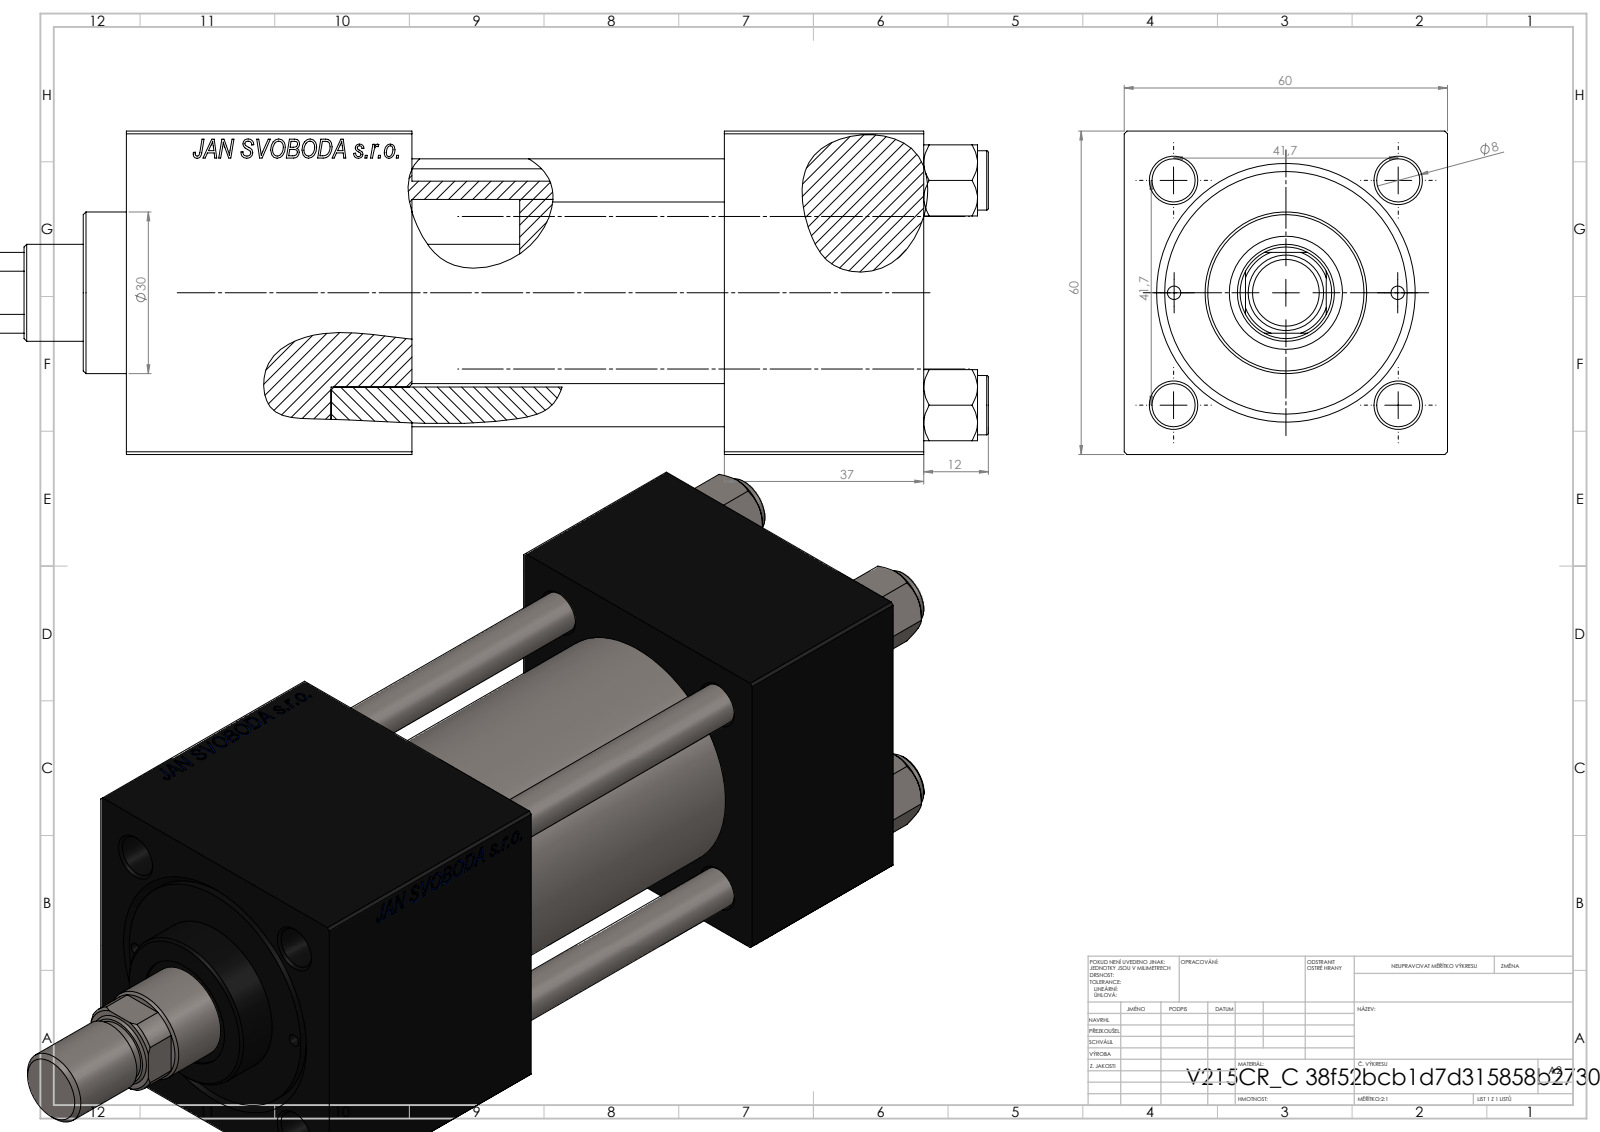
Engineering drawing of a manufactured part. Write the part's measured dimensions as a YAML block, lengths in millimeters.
part_name: "ROD_END_AH; V215CR_C_TYCINKA; V215_VC_A; V215CR_VCP_C (+2 more)"
step_written_by: "SolidWorks 2019 (CONFIG_CONTROL_DESIGN)"
units: millimeters
bodies: {solids: 12, faces: 1168, planar: 532, cylindrical: 94, other: 542}
overall_size: [203, 60, 60]
volume: 405192
surface_area: 106534
round_holes:
  - {diameter: 8, count: 4}
  - {diameter: 2.5, count: 2}
  - {diameter: 7, count: 2}
  - {diameter: 16.66, count: 2}
  - {diameter: 24, count: 2}
  - {diameter: 8.5, count: 1}
  - {diameter: 18, count: 1}
  - {diameter: 21, count: 1}
  - {diameter: 31, count: 1}
  - {diameter: 40, count: 1}
  - {diameter: 45, count: 1}
round_bosses_or_shafts:
  - {diameter: 11, count: 4}
  - {diameter: 46, count: 1}
  - {diameter: 30, count: 1}
  - {diameter: 14, count: 1}
  - {diameter: 12, count: 1}
partial_cylinders:
  - {radius: 8.5, count: 1}
face_to_face_distances: [60, 37, 53, 148, 111, 58, 95, 119.3, 82.3, 24.3]
hole_center_spacings: [20.85, 29.49, 41.7, 46.53, 20.75, 58.97, 41.5, 92.5]
